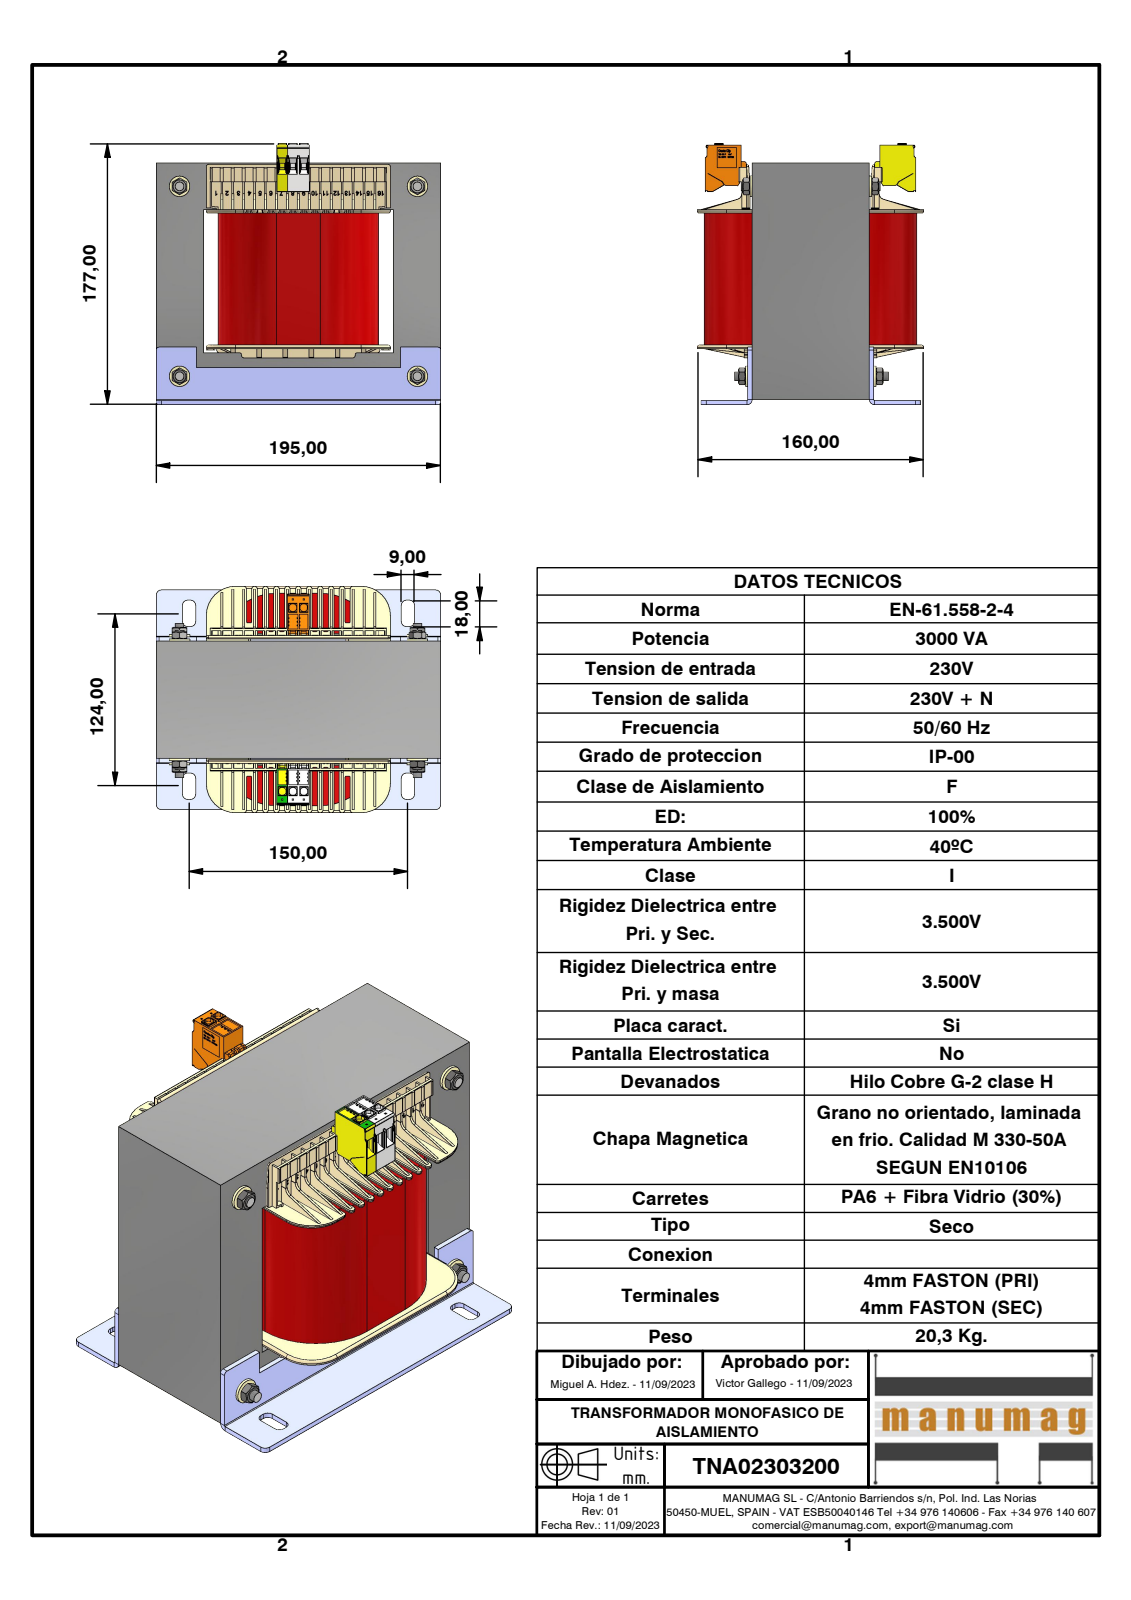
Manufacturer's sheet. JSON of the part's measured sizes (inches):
{"part_name": "TNA02303200; EI195 x 162 - 80 (Rc65); EI192_82_AK_25372_1_Wz837 BOBINADO; EI192_82_AK_25372_1_Wz837 (+8 more)", "step_written_by": "Autodesk Inventor 2023 (AUTOMOTIVE_DESIGN)", "units": "inches", "bodies": {"solids": 28, "faces": 7317, "planar": 5163, "cylindrical": 804, "other": 1350}, "overall_size": [7.677, 7.047, 6.087], "volume_in3": 182.6, "surface_area_in2": 733.2, "round_holes": [[0.194, 4], [0.236, 4], [0.433, 4], [0.39, 2]], "round_bosses_or_shafts": [[0.551, 4], [0.299, 4]], "partial_cylinders_radius": [[0.006, 214], [0.008, 80], [0.039, 52], [0.059, 44], [0.02, 30], [0.077, 22], [0.138, 22], [0.012, 12]], "face_to_face_distances": [5.118, 1.28, 3.15, 6.398, 0.118, 0.094, 3.646, 2.559, 1.26, 3.839], "hole_center_spacings": [5.118, 6.417, 8.208]}
